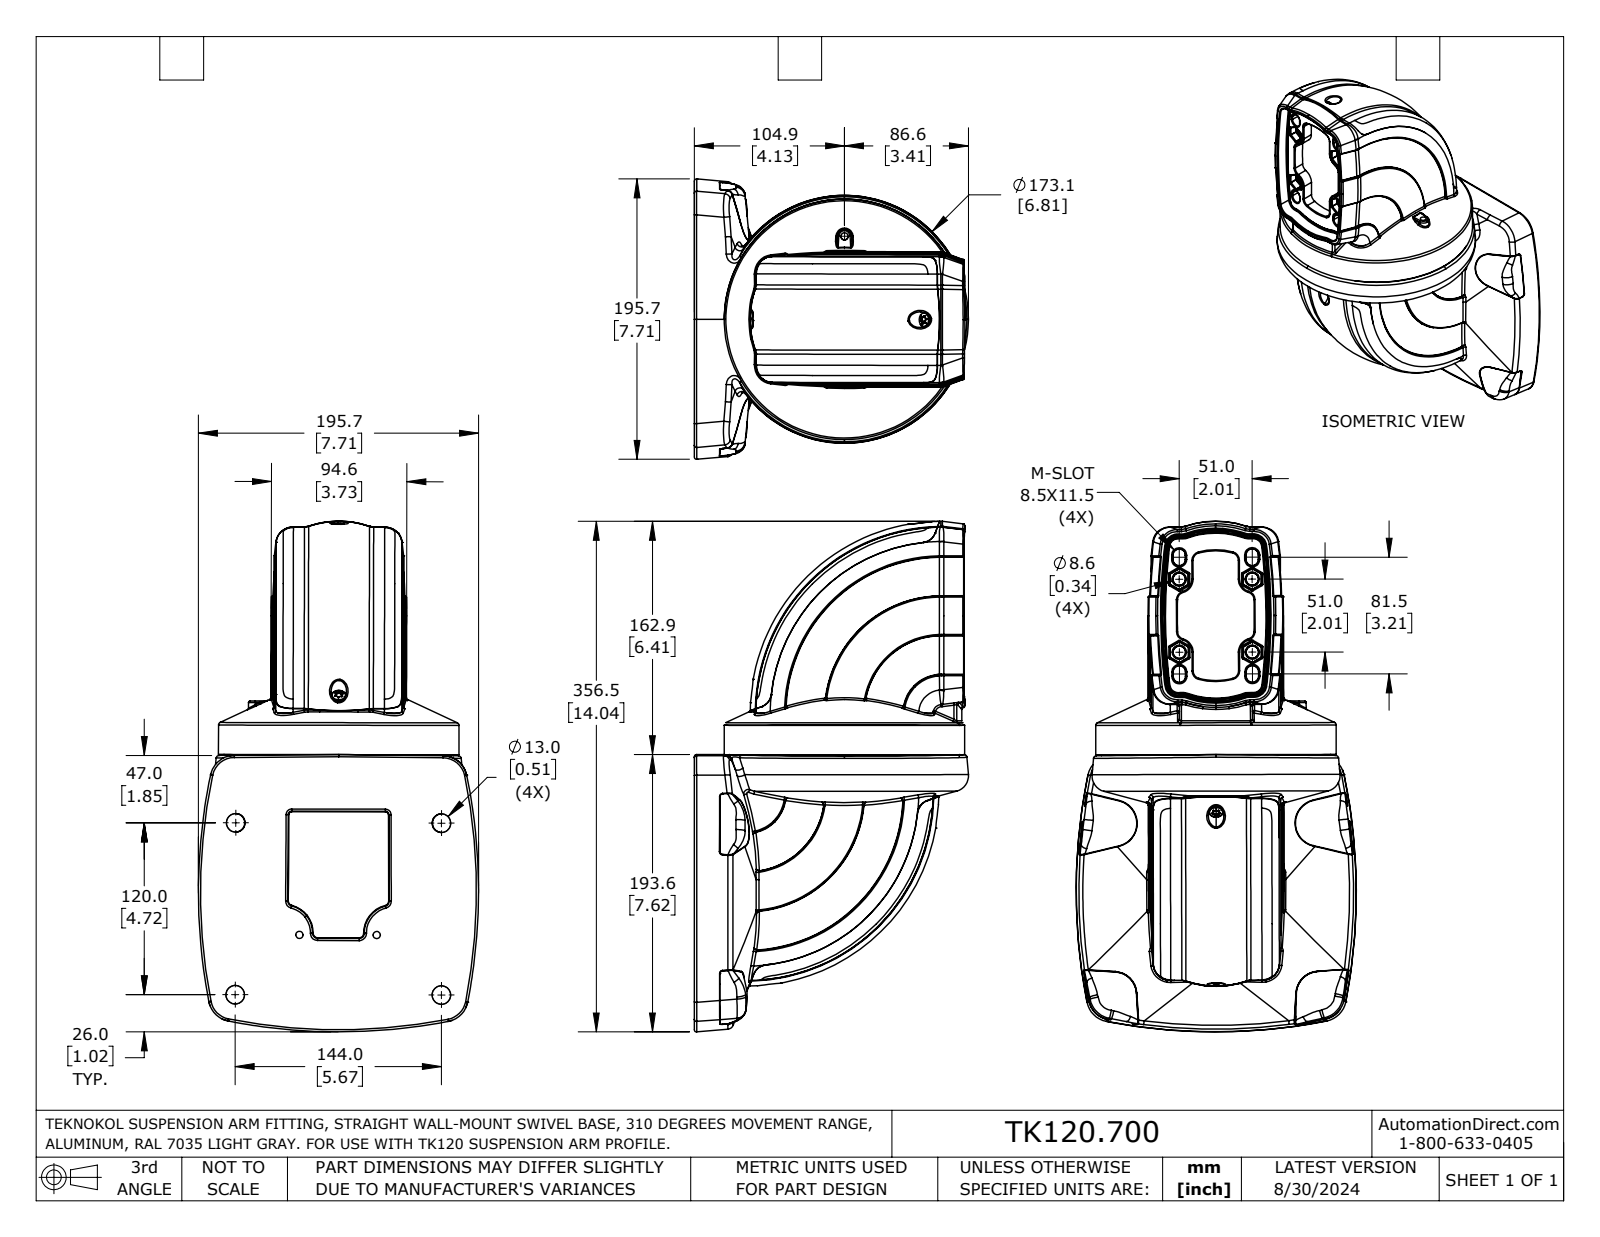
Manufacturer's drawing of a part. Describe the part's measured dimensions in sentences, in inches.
The part is named "TK120.700_REV6". Its 3-D file was written by "SolidWorks 2023 (AUTOMOTIVE_DESIGN)". It is 2 solids with 1511 faces: 158 planar, 189 cylindrical and 1164 other. Overall it measures 14.038 by 7.706 by 7.539 inches. Its volume is 299 cubic inches and its surface area 472.3 square inches. Round holes: 2 of diameter 0.177, 2 of diameter 0.512, 1 of diameter 0.197, 1 of diameter 2.516. Round bosses or shafts: 2 of diameter 0.394, 1 of diameter 6.614, 1 of diameter 6.305, 1 of diameter 0.236. Partial cylindrical surfaces (rounded edges, fillets, slot ends): 48 of radius 0.01, 30 of radius 0.029, 14 of radius 0.004, 12 of radius 0.108, 8 of radius 0.209, 6 of radius 5.112, 5 of radius 0.059, 4 of radius 0.055. The main face-to-face distances are 0.463, 0.404, 6.655, 6.251, 7.038, 6.634, 0.383, 0.512, 6.526, 6.122. The hole center spacings are 1.281, 2.284.
